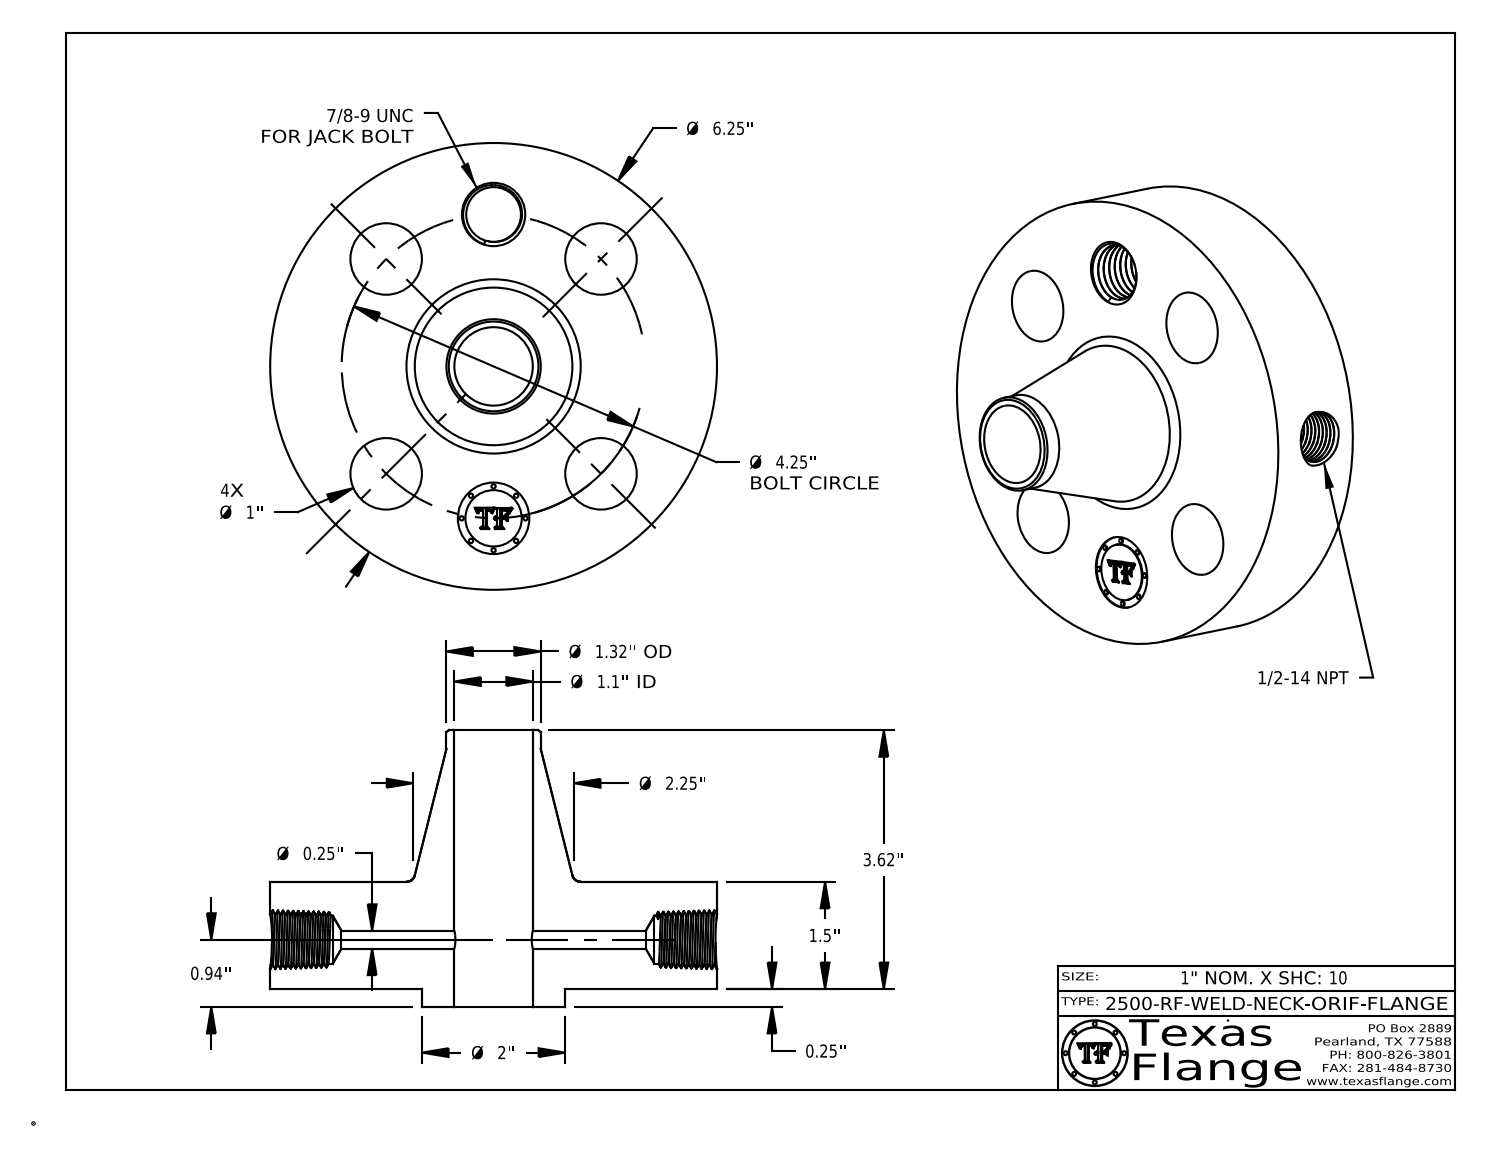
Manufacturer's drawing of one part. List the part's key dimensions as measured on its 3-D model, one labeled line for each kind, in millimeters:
Part name (STEP PRODUCT): 2500-RF-WELD-NECK
STEP written by: CATIA V5 STEP AP214 (AUTOMOTIVE_DESIGN)
Units: millimetres
Bodies: 1 solid, 751 faces (369 planar, 82 cylindrical, 300 other)
Overall size (bounding box): 158.8 × 158.8 × 98.3
Volume: 685 300 mm³ · Surface area: 89 740 mm²
Round holes (diameter × count): ⌀25.4 ×5, ⌀6.4 ×1, ⌀17.1 ×1, ⌀19.5 ×1, ⌀27.9 ×1
Round bosses / shafts (diameter × count): ⌀1.5 ×8, ⌀158.8 ×1, ⌀50.8 ×1, ⌀33.5 ×1, ⌀20 ×1
Main face-to-face distances: 38.1, 6.4, 44.5, 0.4, 44.1, 37.7, 98.3, 91.9, 54.2, 53.8
Hole centre spacings: 54, 41.3, 76.4, 99.7, 108
